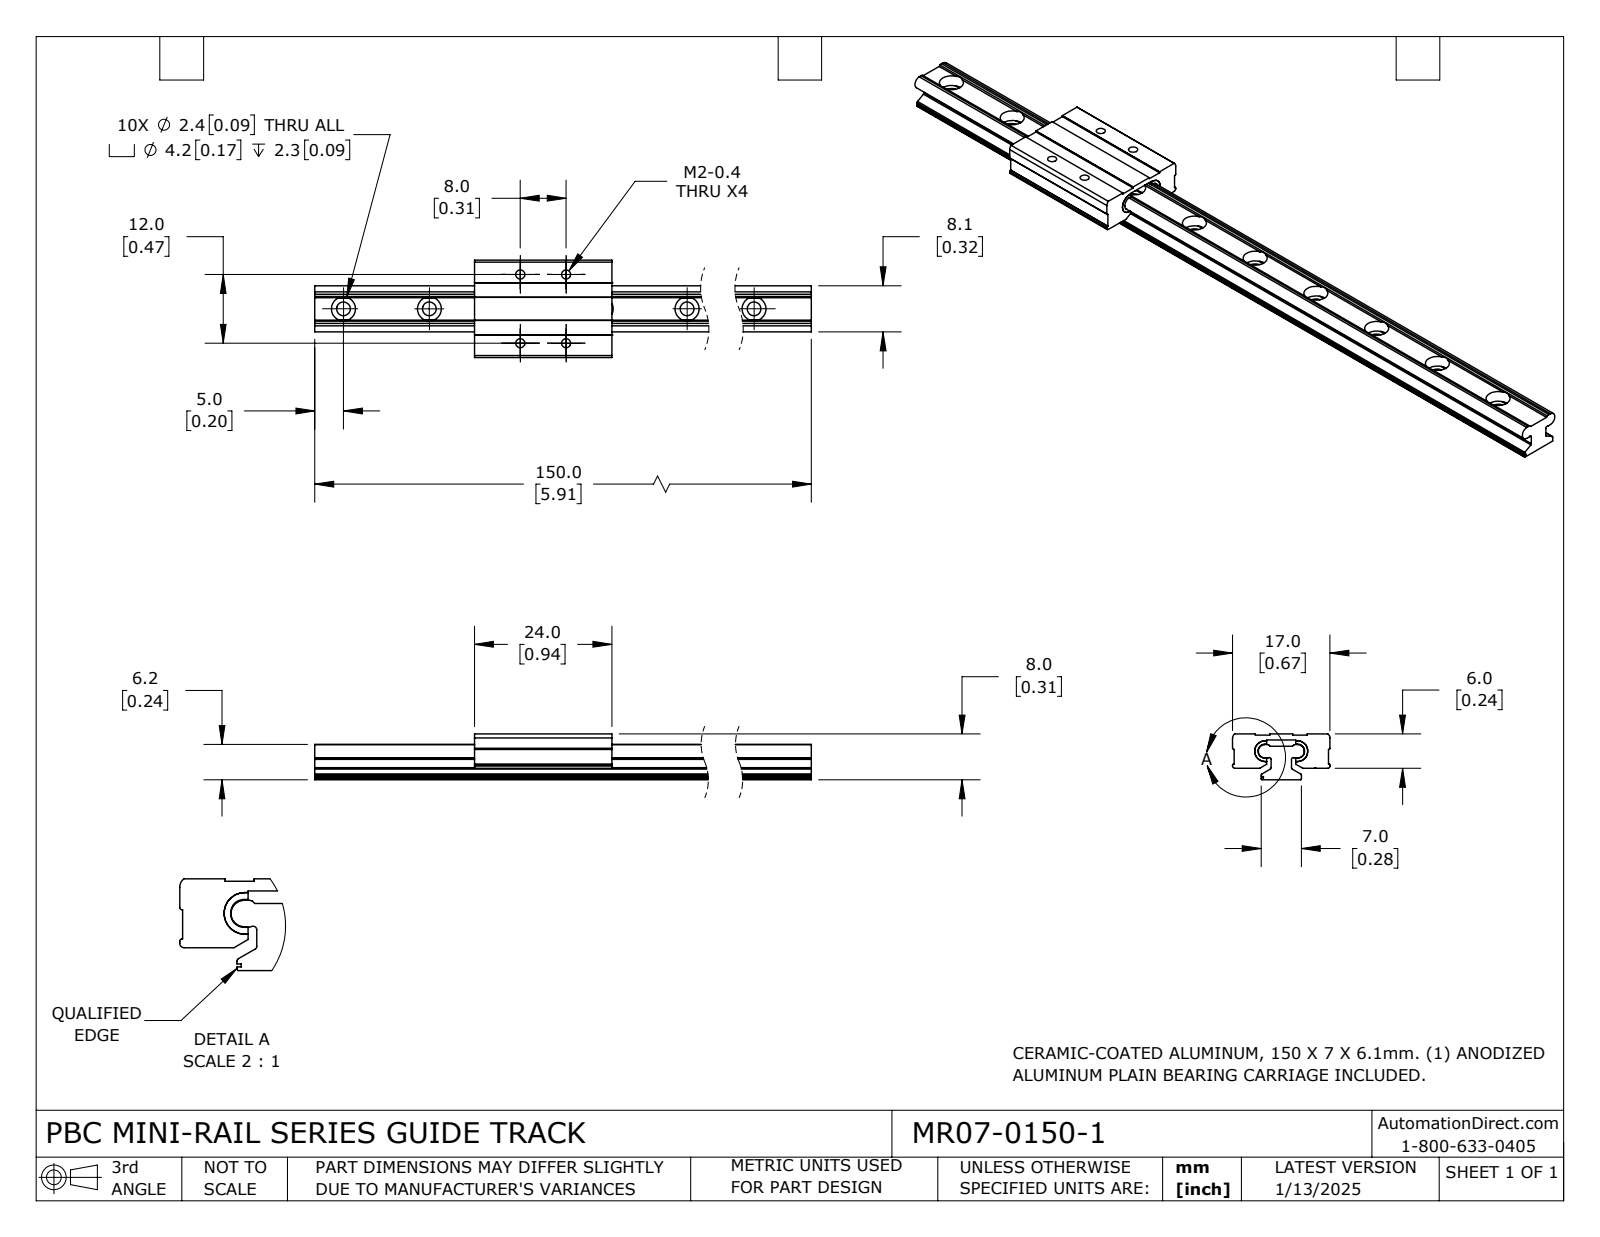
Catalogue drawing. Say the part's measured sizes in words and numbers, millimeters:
The part is named "MR07-0150-1; MR07-0150-1_RAIL; MR07-0150-1_CARRIAGE". Its 3-D file was written by "SolidWorks 2023 (CONFIG_CONTROL_DESIGN)". It is 4 solids with 184 faces: 103 planar, 81 cylindrical and 0 other. Overall it measures 150 by 17 by 8 millimeters. Its volume is 6 340 cubic millimeters and its surface area 7 665 square millimeters. Round holes: 10 of diameter 2.4, 10 of diameter 4.2, 4 of diameter 1.6. Partial cylindrical surfaces (rounded edges, fillets, slot ends): 8 of radius 0.2, 6 of radius 0.3, 4 of radius 1.2, 2 of radius 0.3, 2 of radius 0.4, 2 of radius 0.9, 2 of radius 1.2, 2 of radius 1.8. The main face-to-face distances are 5.9, 8, 2.1, 3.6, 2, 3.9, 6, 1.7, 5.3, 2.8. The hole center spacings are 15, 30, 45, 60, 75, 90, 105, 6.1.
